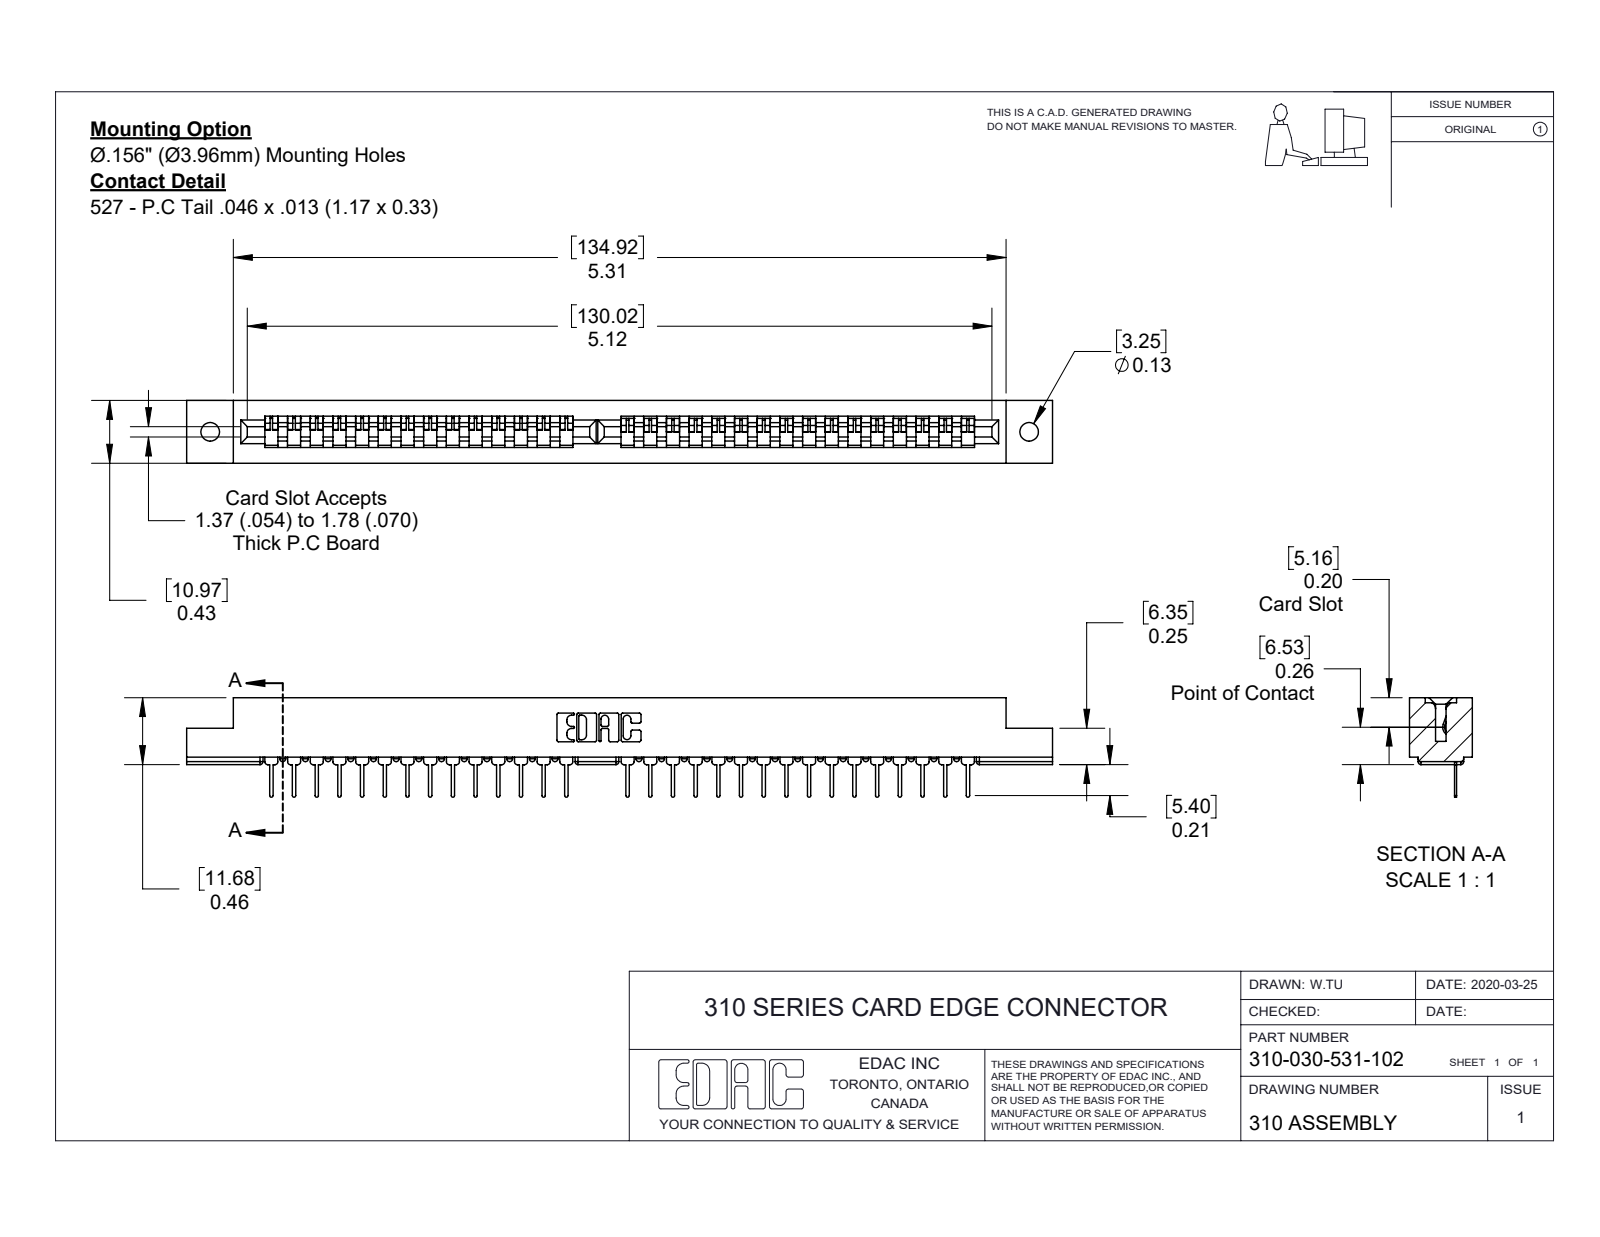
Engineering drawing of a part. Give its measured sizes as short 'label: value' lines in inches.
name: 307-290-001_531; 310 Part_.128 Dia. Hole; 310-030-531-102
written by: SolidWorks 2016 (CONFIG_CONTROL_DESIGN)
unit: in
bodies: 31 solids, 1846 faces (1194 planar, 588 cylindrical, 64 other)
size: 5.953 × 0.684 × 0.432
volume: 0.767 in³; area: 22.21 in²
holes: 2× ⌀0.128
rounds: 158× R0.02, 30× R0.011, 22× R0.01, 6× R0.007, 6× R0.031, 3× R0.026, 2× R0.012, 2× R0.025
face distances: 0.109, 0.324, 0.432, 0.072, 0.015, 0.013, 0.409, 0.215, 0.18, 0.252
hole spacings: 5.63
